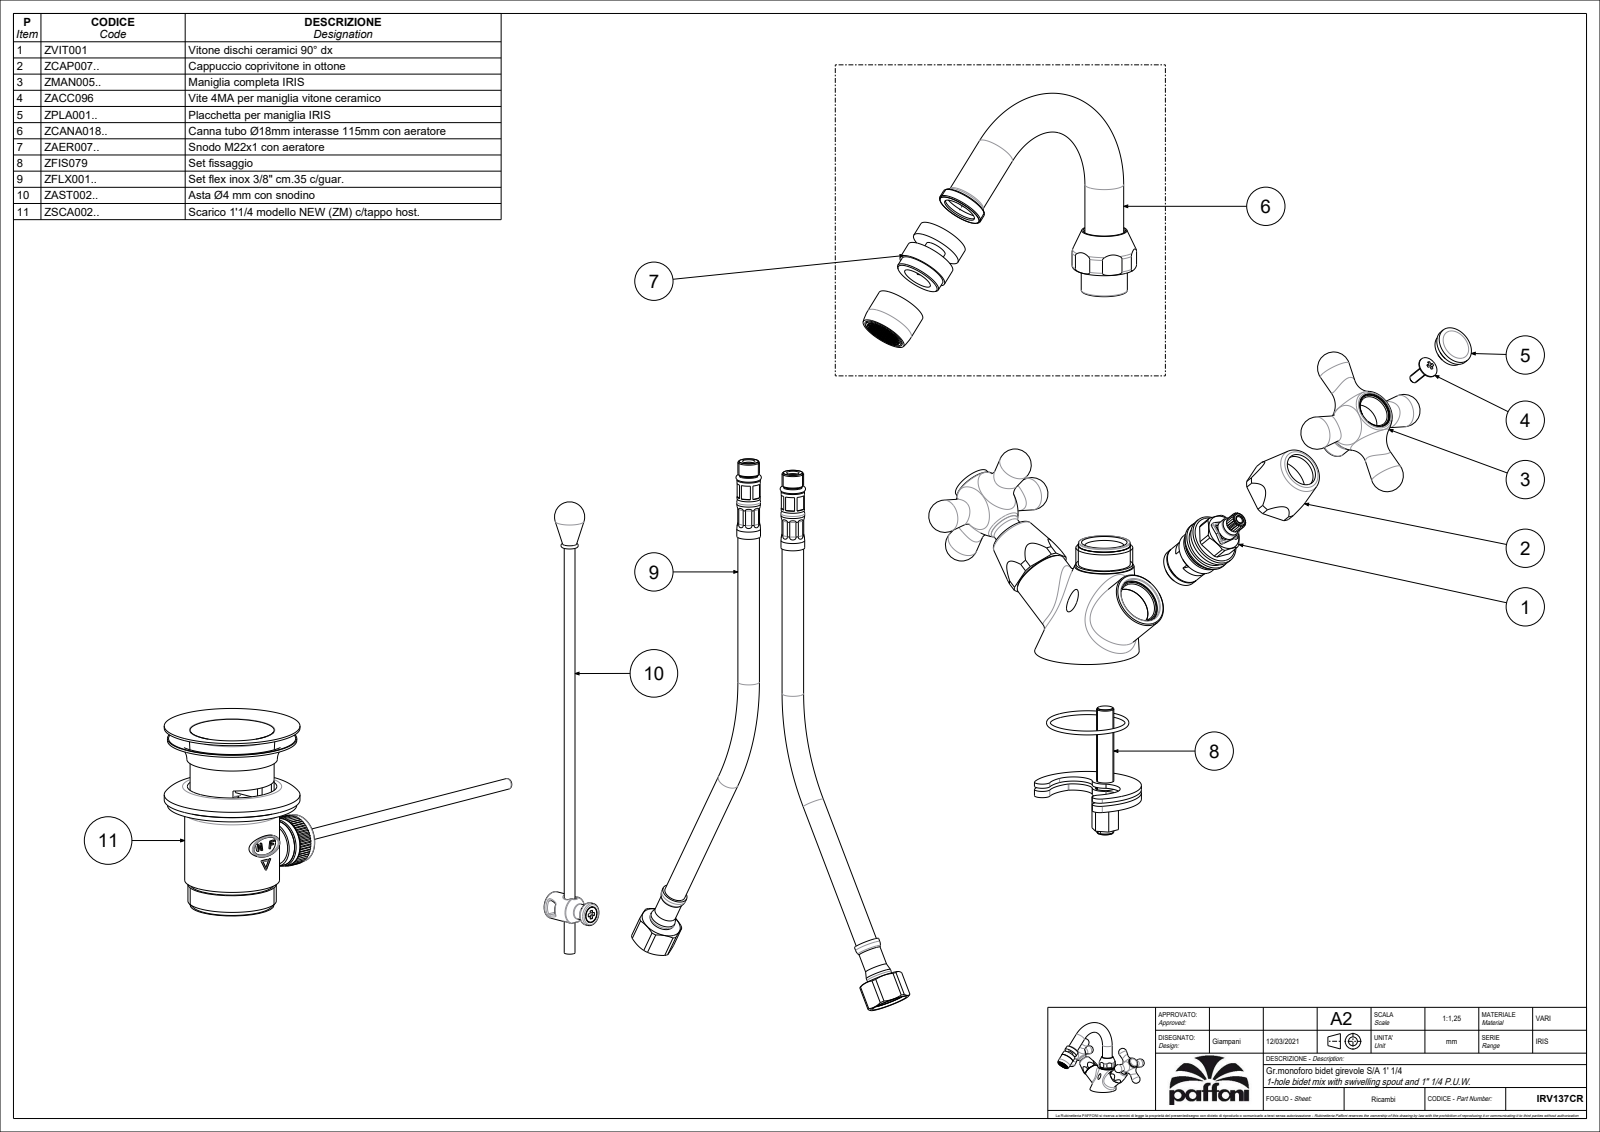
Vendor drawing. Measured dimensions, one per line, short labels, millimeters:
name: IRV137CR
written by: CREO PARAMETRIC BY PTC INC, 2020044 (CONFIG_CONTROL_DESIGN)
unit: mm
bodies: 2 solids, 485 faces (142 planar, 116 cylindrical, 227 other)
size: 183.98 × 151.19 × 132.5
volume: 167 211 mm³; area: 54 133 mm²
holes: 4× ⌀9, 2× ⌀8, 2× ⌀11, 2× ⌀15.7, 2× ⌀18, 2× ⌀19, 2× ⌀21, 2× ⌀21.5, 2× ⌀23, 1× ⌀5.5, 1× ⌀6, 1× ⌀6.8
bosses: 4× ⌀18, 2× ⌀26.3, 2× ⌀13.5, 1× ⌀34, 1× ⌀26.4, 1× ⌀24, 1× ⌀23.6, 1× ⌀18.8
rounds: 2× R14.5, 1× R15
face distances: 26.49, 22, 5, 24.01, 28.5, 23.7, 28.7, 1.3, 46.01, 41.7
hole spacings: 7, 11.8, 13.38, 13.89, 0.6, 9.5, 11.4, 12
